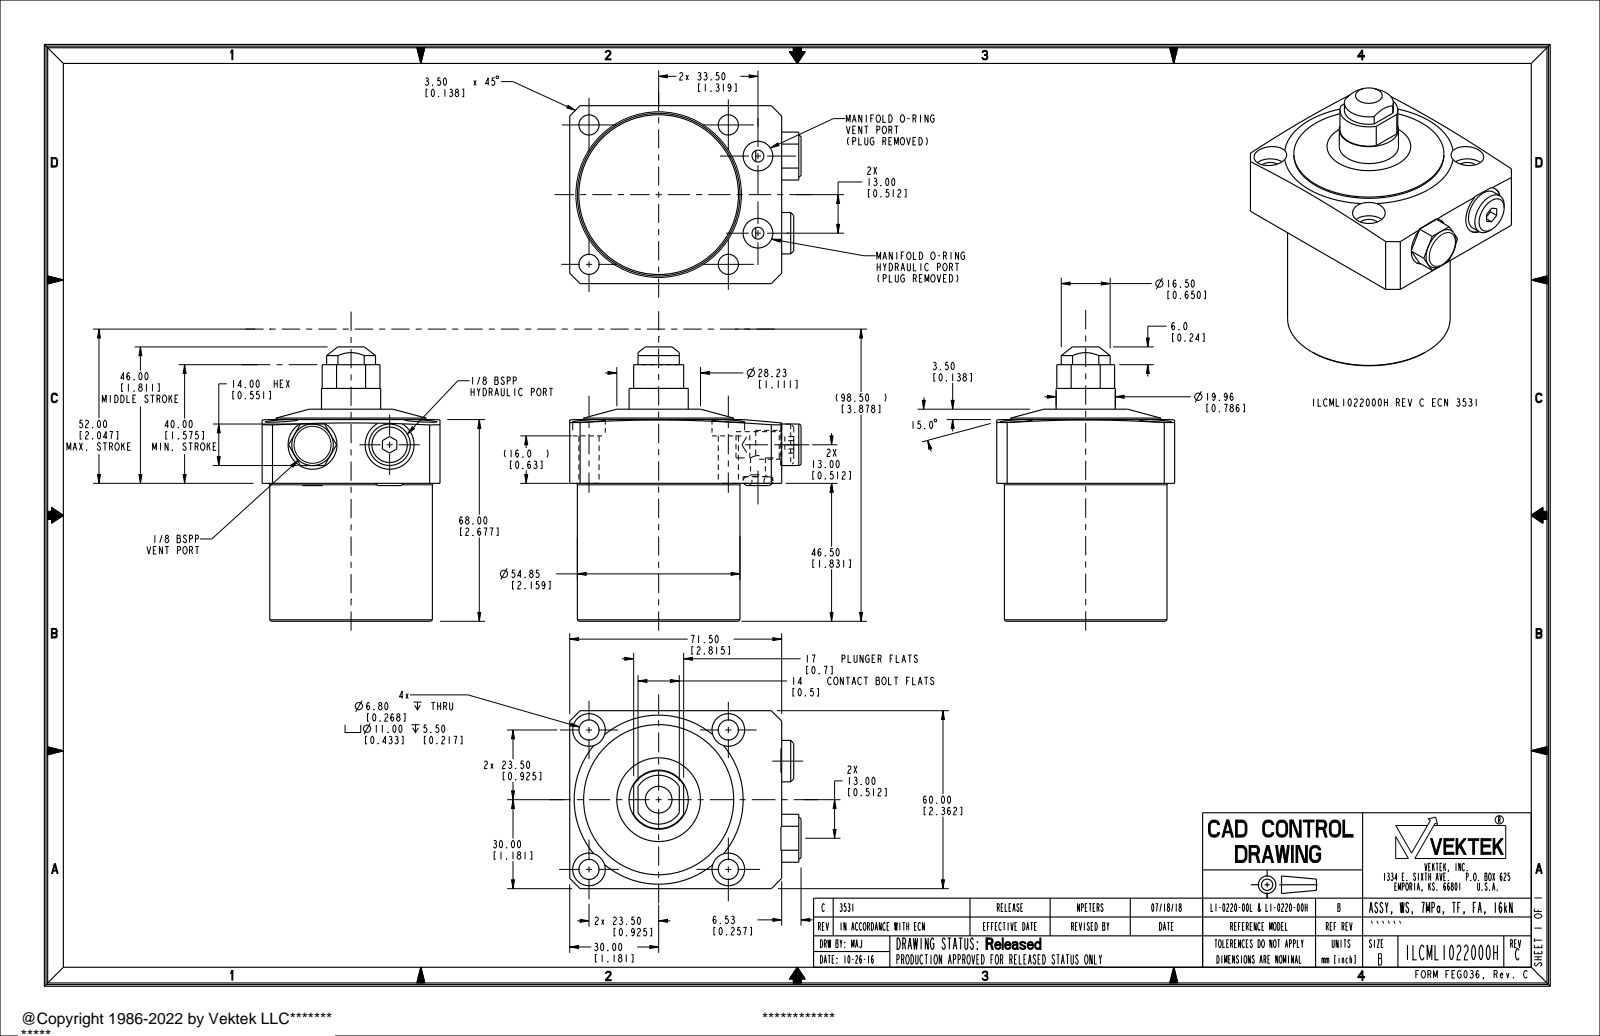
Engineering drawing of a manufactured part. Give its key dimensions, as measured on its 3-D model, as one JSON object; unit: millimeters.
{"part_name": "ILCML1022000H", "step_written_by": "PRO/ENGINEER BY PARAMETRIC TECHNOLOGY CORPORATION, 2013320 (AUTOMOTIVE_DESIGN)", "units": "millimeters", "bodies": {"solids": 4, "faces": 137, "planar": 55, "cylindrical": 50, "other": 32}, "overall_size": [92.5, 78.03, 60], "volume_mm3": 205838, "surface_area_mm2": 27930, "round_holes": [[6.8, 4], [11, 4], [5, 2], [6, 2], [8.84, 2], [10, 2], [16.5, 2]], "round_bosses_or_shafts": [[54.85, 1], [50.62, 1], [19.96, 1], [13.97, 1], [9.73, 1], [9.72, 1]], "partial_cylinders_radius": [[8.25, 1], [9.75, 1]], "face_to_face_distances": [46.5, 60, 71.5, 68, 21.5, 25, 3.5, 71.25, 16, 62.5], "hole_center_spacings": [47, 14.5, 26, 37.85, 57.96, 66.47, 67.68]}
